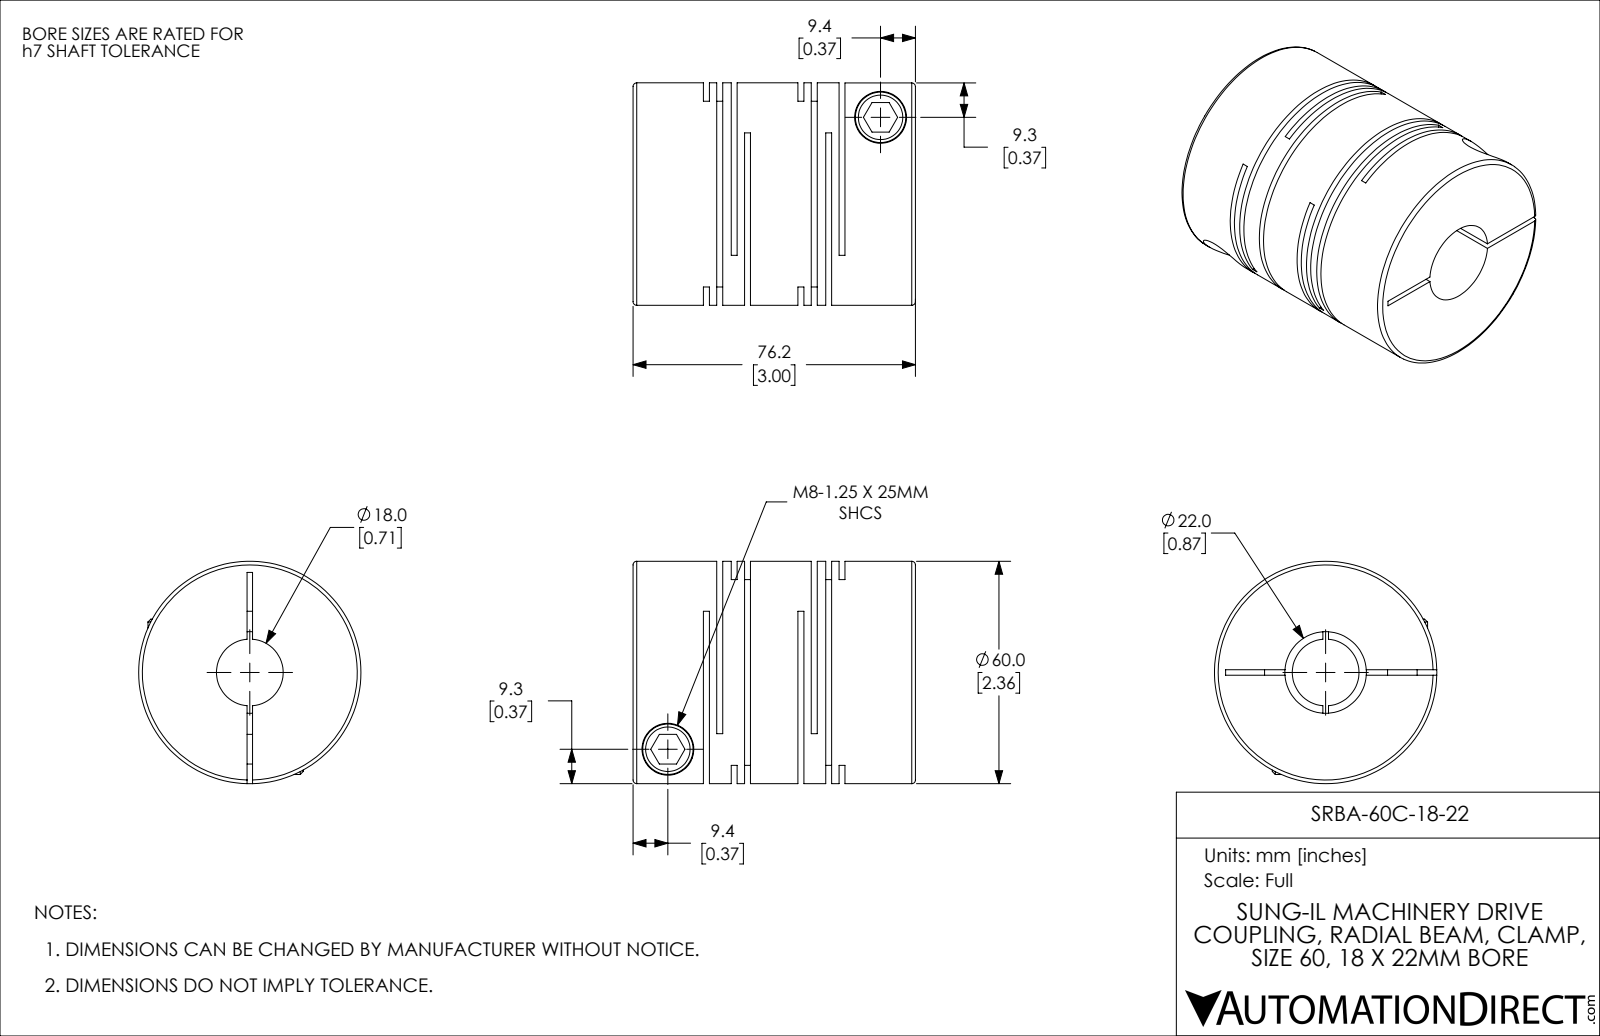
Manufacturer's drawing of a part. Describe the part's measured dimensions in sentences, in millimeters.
The part is named "SRBA-60C-18-22". Its 3-D file was written by "SolidWorks 2021 (CONFIG_CONTROL_DESIGN)". It is 1 solid with 115 faces: 60 planar, 42 cylindrical and 13 other. Overall it measures 76.2 by 60 by 60 millimeters. Its volume is 158 500 cubic millimeters and its surface area 58 350 square millimeters. Round holes: 2 of diameter 8, 2 of diameter 14, 1 of diameter 18, 1 of diameter 22. Round bosses or shafts: 2 of diameter 13.6, 1 of diameter 60. The main face-to-face distances are 1.6, 3.6, 7.5, 25.5, 33, 27.1, 18, 2, 5.9, 23.9.
